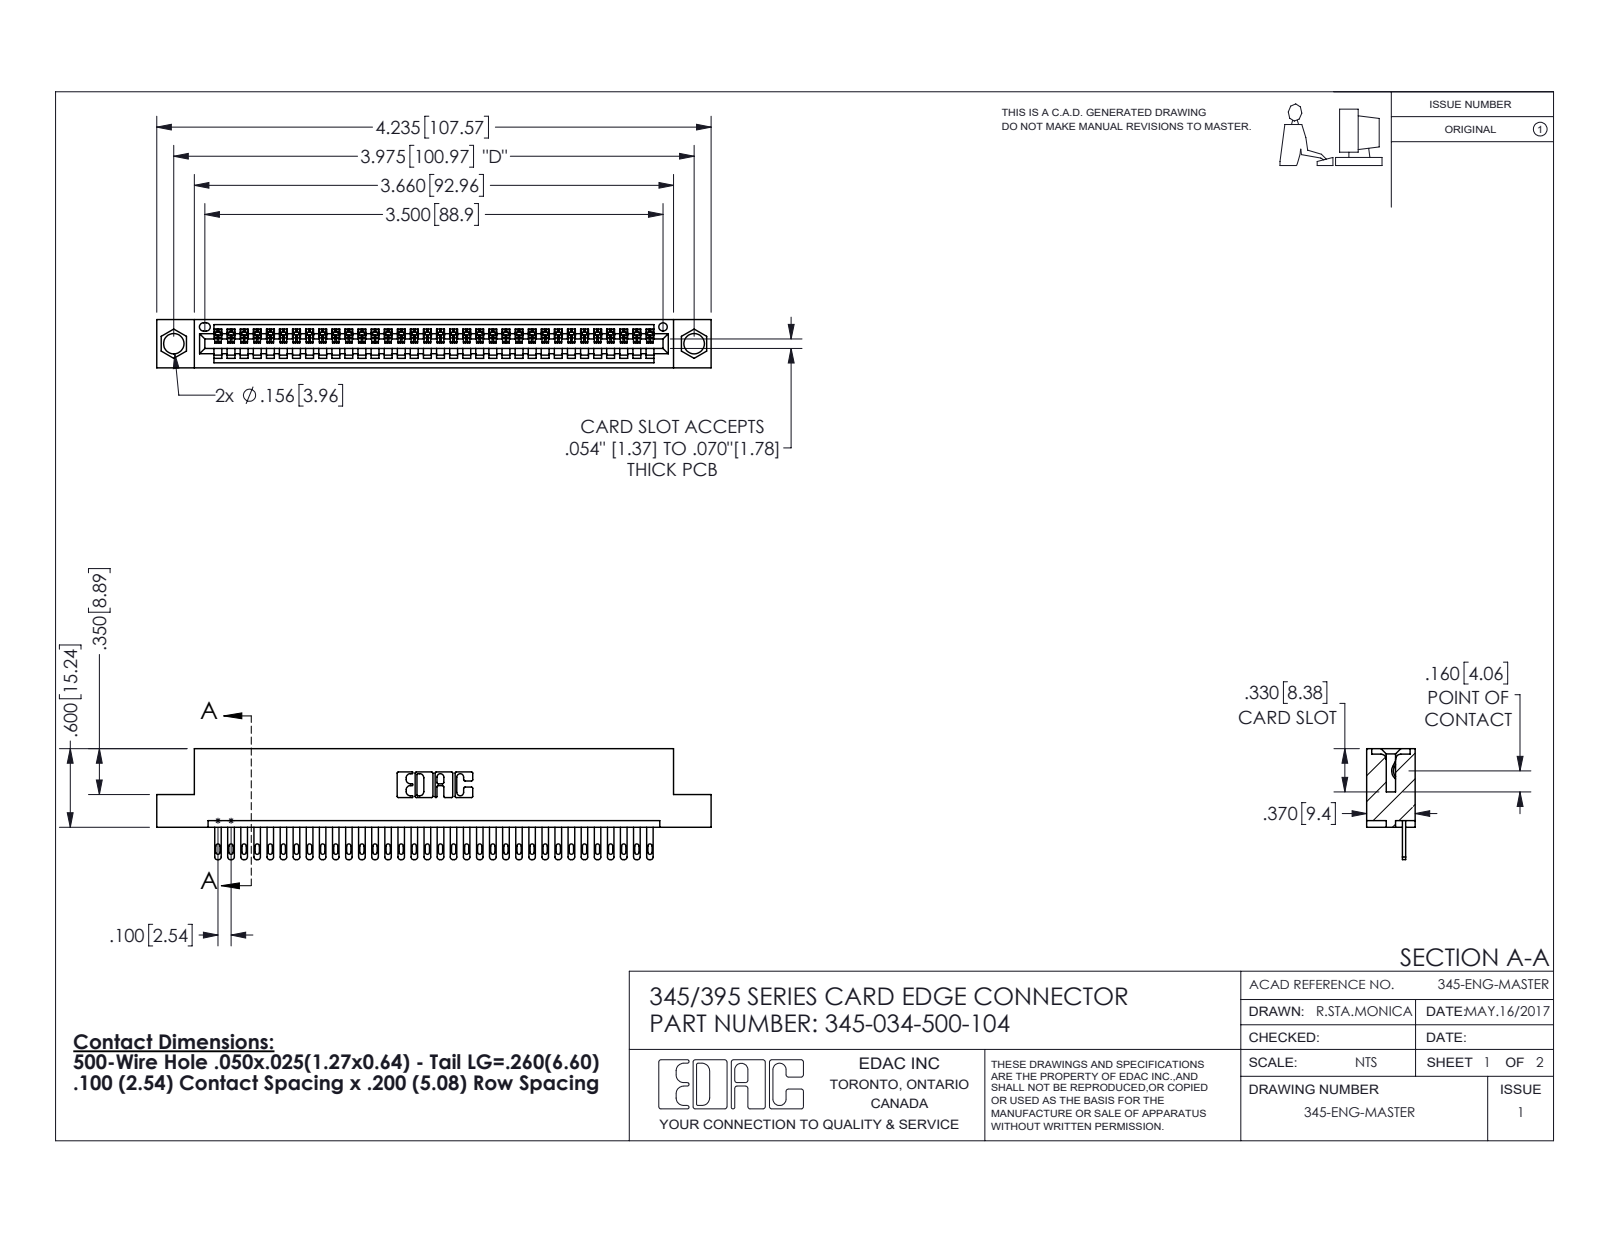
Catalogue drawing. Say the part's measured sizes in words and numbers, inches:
The part is named "345-292-001_345-293-100; 345-034-500-104; 345 Part_Flush Mounting Lugs - 0.156 Dia-TH". Its 3-D file was written by "SolidWorks 2016 (CONFIG_CONTROL_DESIGN)". It is 35 solids with 1962 faces: 1236 planar, 726 cylindrical and 0 other. Overall it measures 4.235 by 0.847 by 0.37 inches. Its volume is 0.615 cubic inches and its surface area 20.43 square inches. Round holes: 2 of diameter 0.156, 1 of diameter 0.064. Partial cylindrical surfaces (rounded edges, fillets, slot ends): 68 of radius 0.006, 68 of radius 0.016, 68 of radius 0.02, 22 of radius 0.01, 6 of radius 0.007, 6 of radius 0.031, 3 of radius 0.026, 2 of radius 0.031. The main face-to-face distances are 0.298, 0.072, 0.2, 0.37, 0.098, 0.272, 0.025, 0.225, 0.149, 0.072. The hole center spacings are 0.27, 3.74, 3.975.
